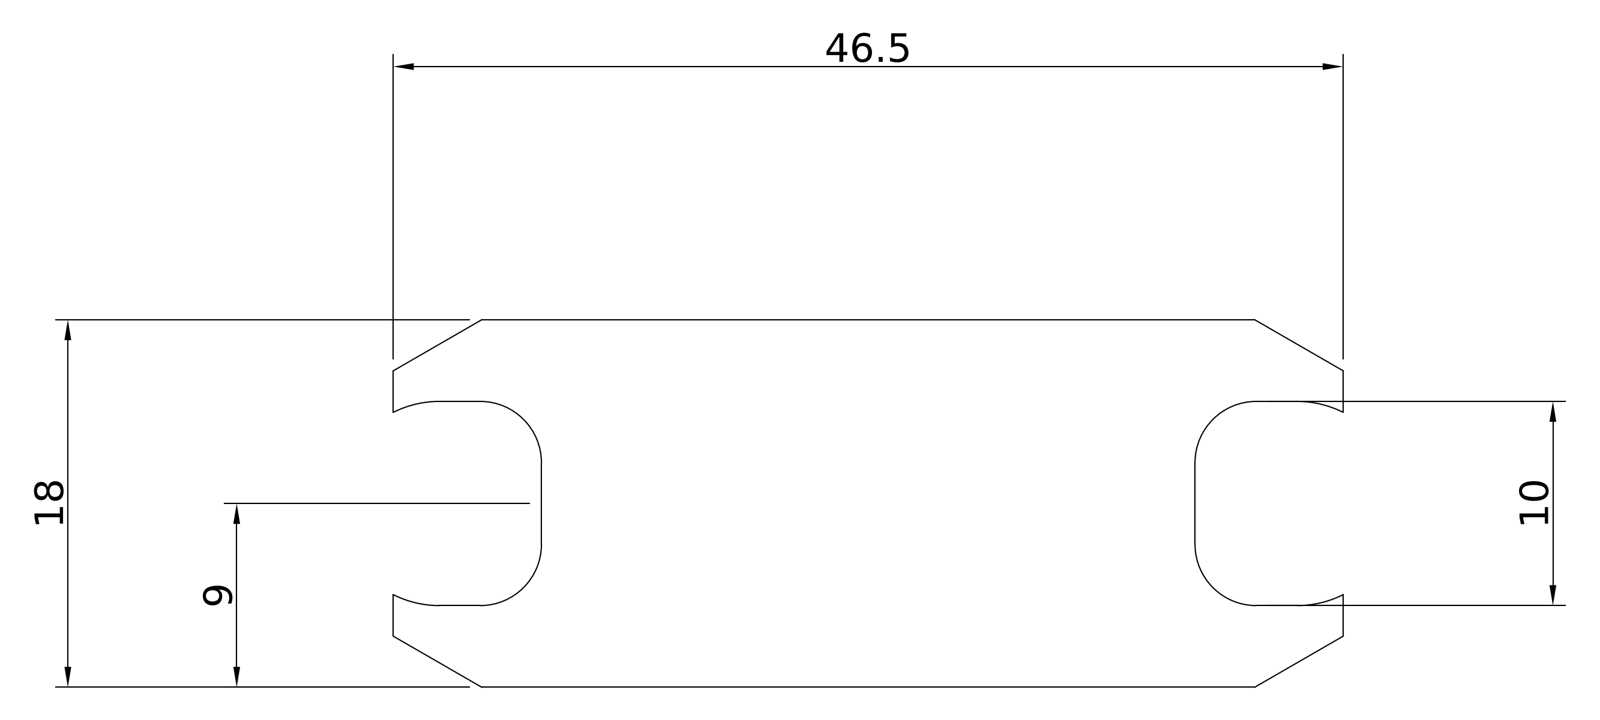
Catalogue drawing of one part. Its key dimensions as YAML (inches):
part_name: "DM80PGL0014-A; 952510020102; 952510020103"
step_written_by: "Autodesk Inventor 2022 (AUTOMOTIVE_DESIGN)"
units: inches
bodies: {solids: 3, faces: 32, planar: 22, cylindrical: 10, other: 0}
overall_size: [3.937, 2.047, 0.709]
volume: 5.106
surface_area: 35.27
round_holes:
  - {diameter: 0.394, count: 2}
partial_cylinders:
  - {radius: 0.118, count: 4}
face_to_face_distances: [0.709, 1.358, 3.937, 0.157, 0.551, 0.285, 1.545, 1.831, 0.394, 1.26]
hole_center_spacings: [1.654]
